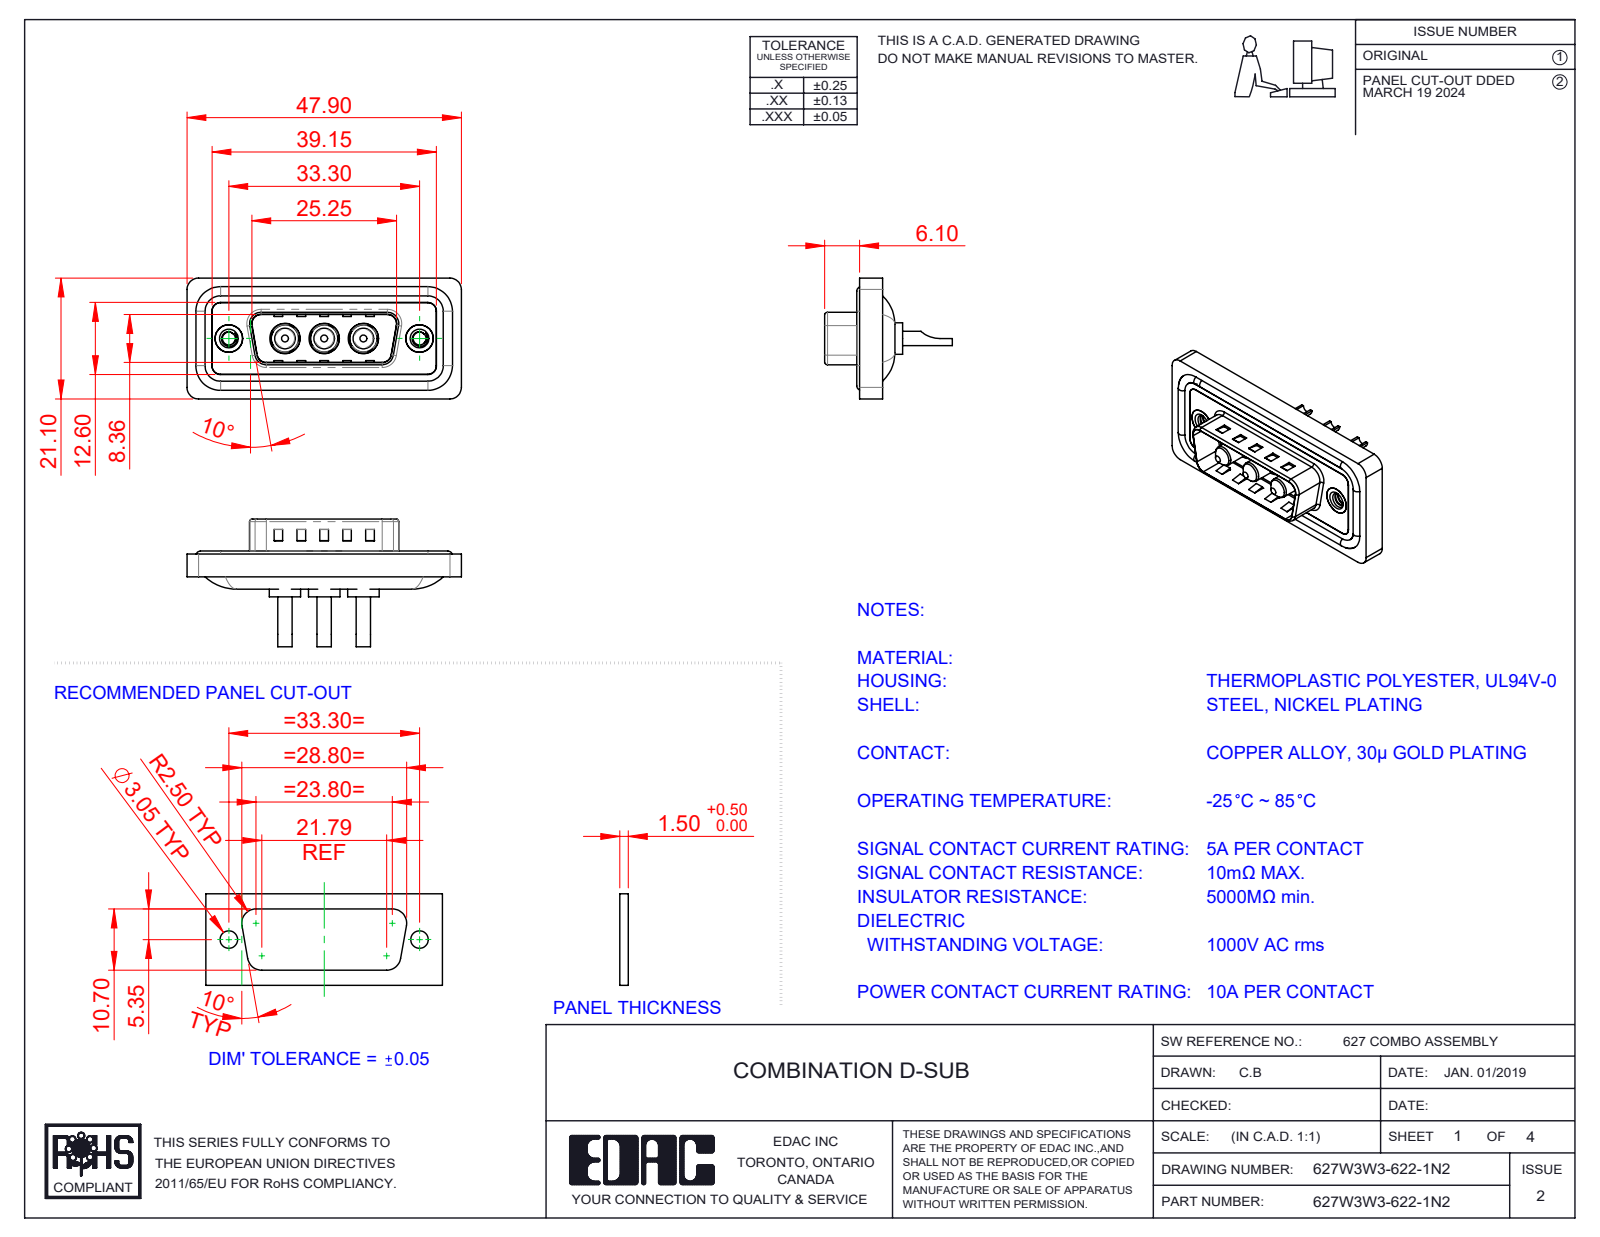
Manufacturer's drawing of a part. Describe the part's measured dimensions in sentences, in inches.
The part is named "627Combo Shell Rear_15 Contacts; Power Pin_10A SC; 627Combo Waterproof Housing_15 Contacts; 627Combo Housing_3W3 (+3 more)". Its 3-D file was written by "SolidWorks 2023 (CONFIG_CONTROL_DESIGN)". It is 13 solids with 582 faces: 213 planar, 250 cylindrical and 119 other. Overall it measures 1.886 by 0.878 by 0.831 inches. Its volume is 0.34 cubic inches and its surface area 13.79 square inches. Round holes: 3 of diameter 0.067, 3 of diameter 0.191, 3 of diameter 0.209, 2 of diameter 0.089, 2 of diameter 0.157, 2 of diameter 0.189, 2 of diameter 0.197. Round bosses or shafts: 4 of diameter 0.063, 3 of diameter 0.217, 3 of diameter 0.205, 3 of diameter 0.187, 3 of diameter 0.148, 3 of diameter 0.142, 3 of diameter 0.098, 2 of diameter 0.193. Partial cylindrical surfaces (rounded edges, fillets, slot ends): 26 of radius 0.059, 20 of radius 0.079, 8 of radius 0.02, 8 of radius 0.063, 4 of radius 0.01, 4 of radius 0.024, 4 of radius 0.026, 4 of radius 0.035. The main face-to-face distances are 0.016, 0.043, 0.059, 0.02, 0.063, 0.122, 0.114, 0.157, 0.032, 0.377. The hole center spacings are 0.27, 0.386, 0.656, 0.925, 0.539, 1.311.
